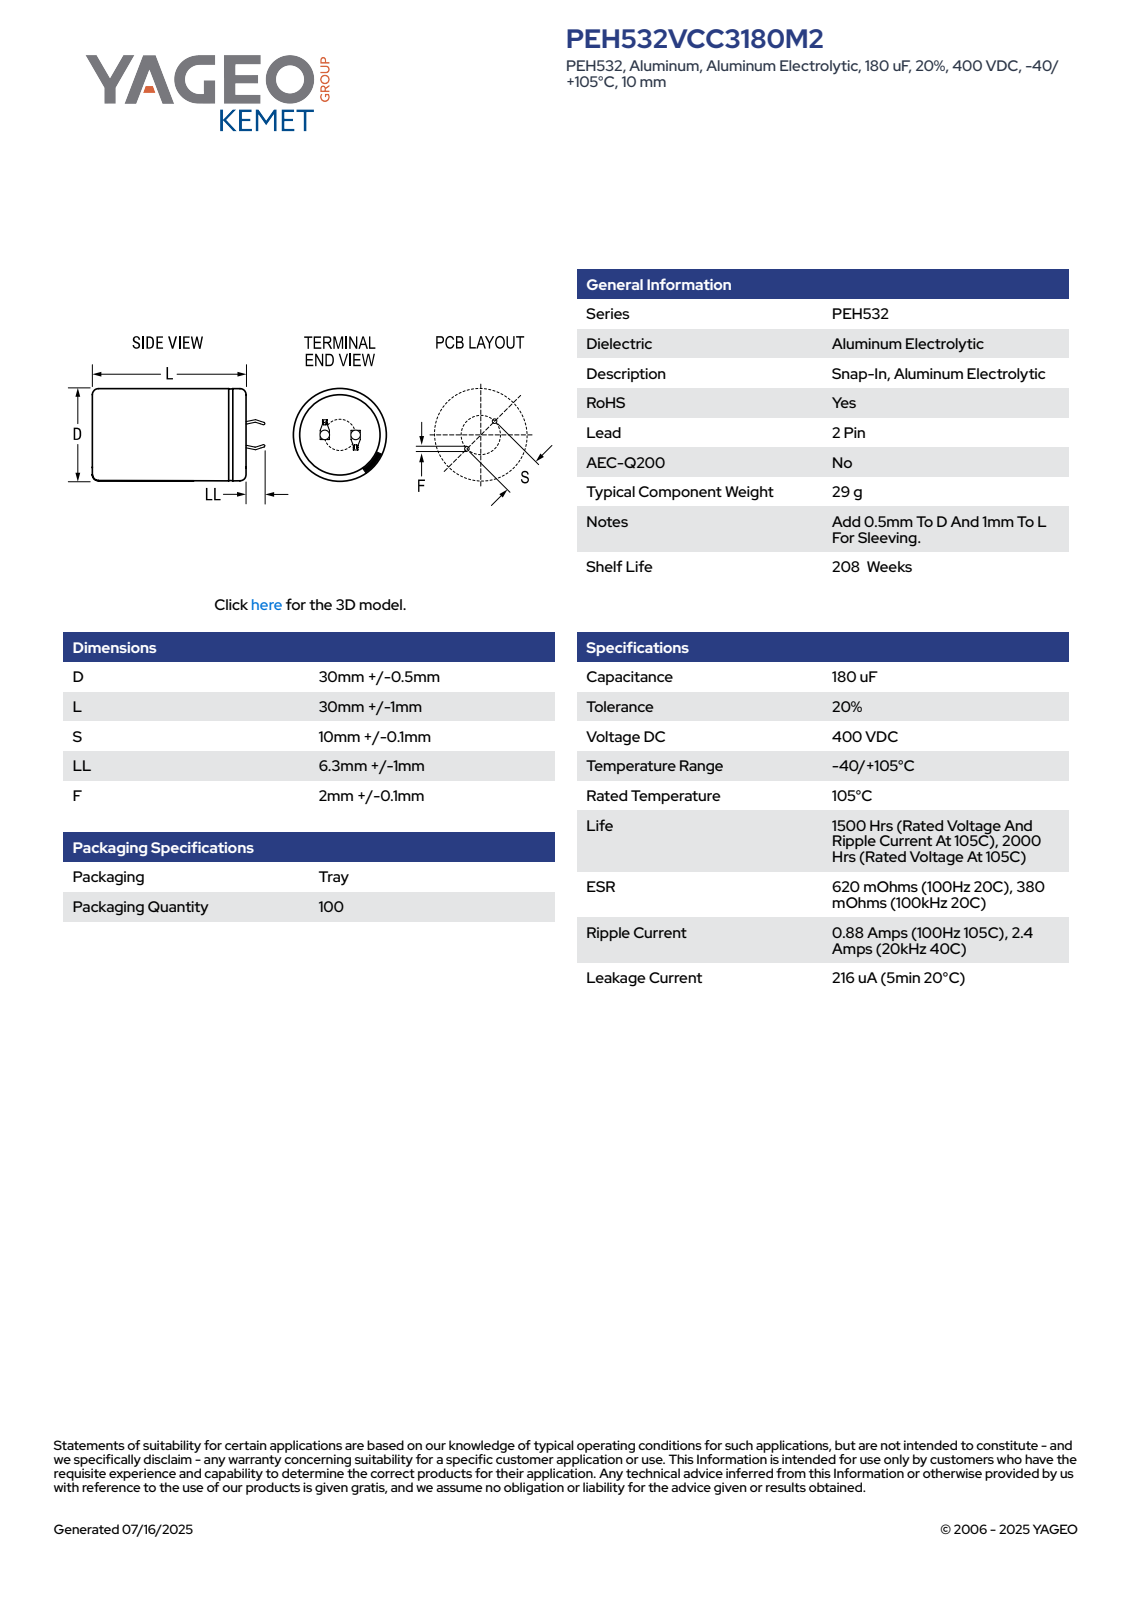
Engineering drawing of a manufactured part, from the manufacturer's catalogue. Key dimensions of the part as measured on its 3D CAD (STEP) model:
Part name (STEP PRODUCT): CARS_K2P_30X30_D30.5L31S10LL7.3F2.1
STEP written by: SolidWorks 2014 (AUTOMOTIVE_DESIGN)
Units: millimetres
Bodies: 1 solid, 100 faces (52 planar, 9 cylindrical, 39 other)
Overall size (bounding box): 38.29 × 30.5 × 30.5
Volume: 22 332 mm³ · Surface area: 4 443 mm²
Round holes (diameter × count): ⌀26.99 ×1
Round bosses / shafts (diameter × count): ⌀30.5 ×1
Partial cylindrical surfaces — rounded edges, fillets, slot ends (radius × count): R15.24 ×1
Main face-to-face distances: 30.99, 0.6, 31.49, 0.5, 7.08, 7.64, 0.75, 1.35, 7.68, 6.48
